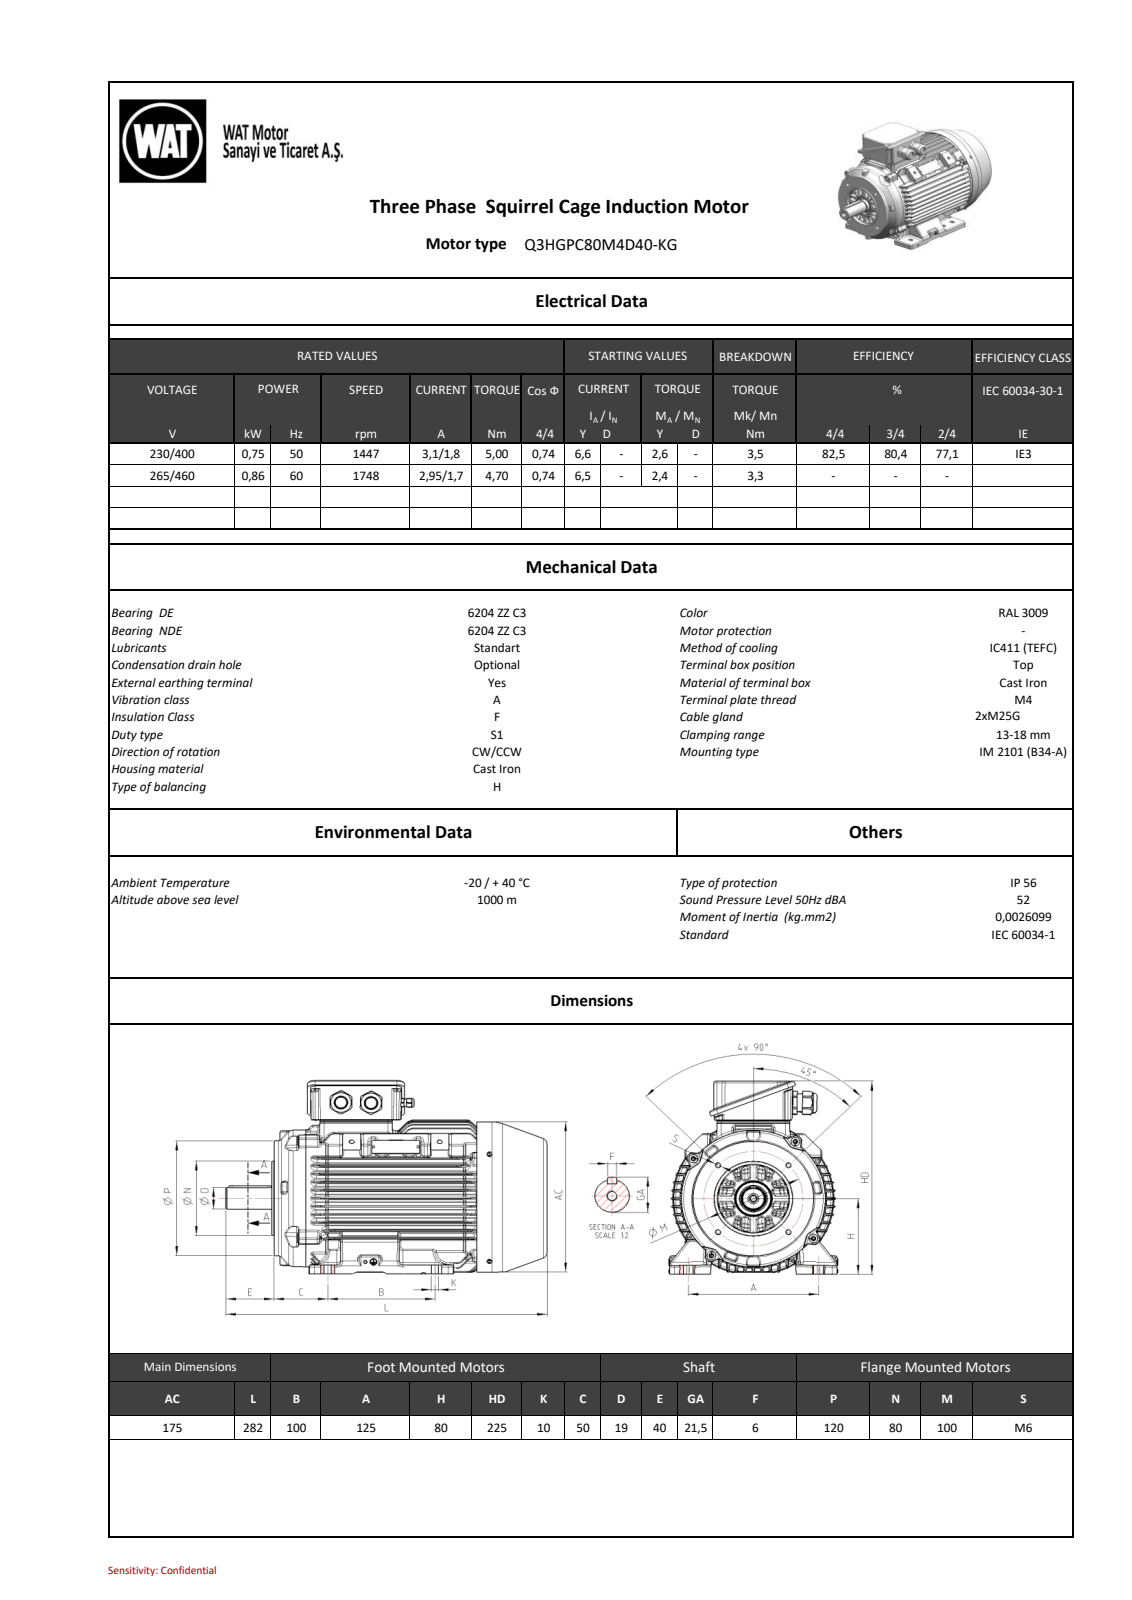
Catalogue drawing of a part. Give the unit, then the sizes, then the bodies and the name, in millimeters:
Units: millimetres
Overall size (bounding box): 281.71 × 224.98 × 221.33
Round holes (diameter × count): ⌀5 ×4, ⌀10 ×3, ⌀2.5 ×2, ⌀3.3 ×2, ⌀17.2 ×2, ⌀6.4 ×1, ⌀6.5 ×1, ⌀27.8 ×1, ⌀28 ×1, ⌀168 ×1
Round bosses / shafts (diameter × count): ⌀20 ×4, ⌀9.2 ×3, ⌀8.65 ×3, ⌀8.5 ×3, ⌀8 ×3, ⌀5 ×3, ⌀27.7 ×2, ⌀25.25 ×2
Partial cylindrical surfaces — rounded edges, fillets, slot ends (radius × count): R1.5 ×287, R2.5 ×40, R1.8 ×38, R1 ×30, R4 ×26, R2 ×23, R5 ×22, R0.2 ×18
Main face-to-face distances: 41.78, 62.56, 241.71, 199.93, 3.01, 1.5, 3, 152.95, 215.51, 1.53
Hole centre spacings: 70.71, 50, 100, 40, 49.99, 50.01, 74.99, 77.95
Bodies: 0 solids, 2817 faces (767 planar, 785 cylindrical, 1265 other)
Part name (STEP PRODUCT): 26000A30F4D8rop6
STEP written by: SIEMENS PLM Software NX 11.0 (AUTOMOTIVE_DESIGN)
